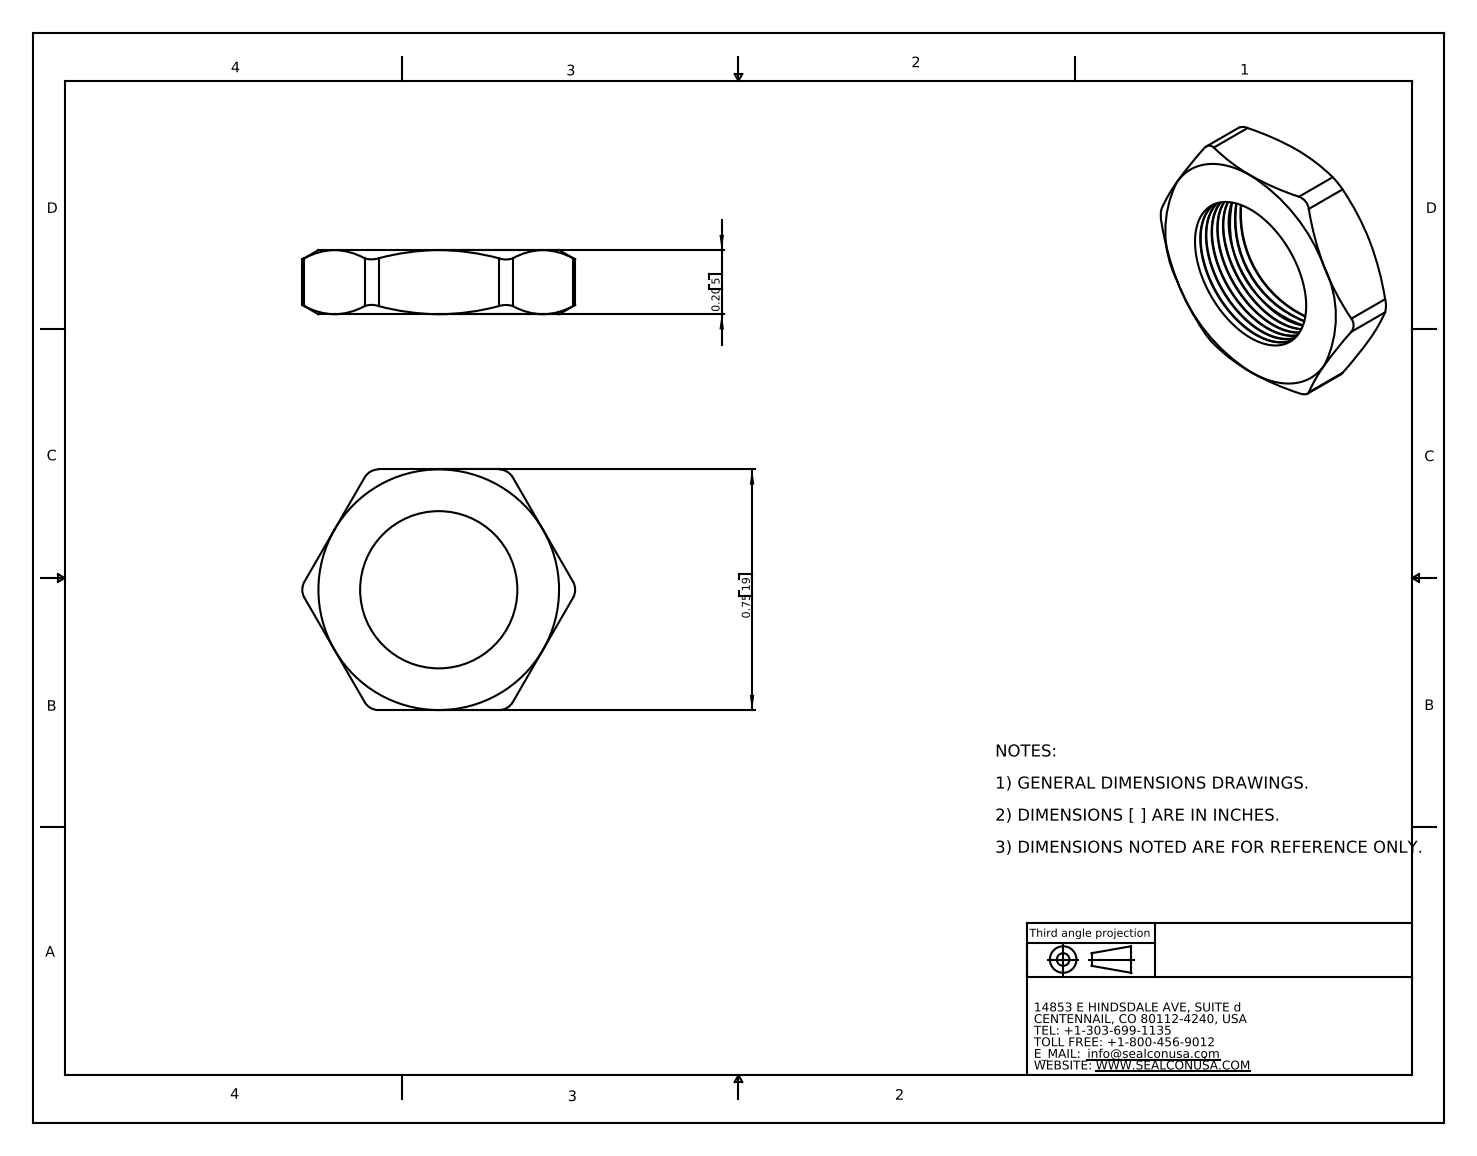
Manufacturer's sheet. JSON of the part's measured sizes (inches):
{"part_name": "NP-07-GY", "step_written_by": "SolidWorks 2007 (CONFIG_CONTROL_DESIGN)", "units": "inches", "bodies": {"solids": 1, "faces": 77, "planar": 8, "cylindrical": 23, "other": 46}, "overall_size": [0.851, 0.75, 0.2], "volume_in3": 0.056, "surface_area_in2": 1.681, "round_holes": [[0.49, 1]], "partial_cylinders_radius": [[0.05, 6]], "face_to_face_distances": [0.2, 0.75, 0.75]}
